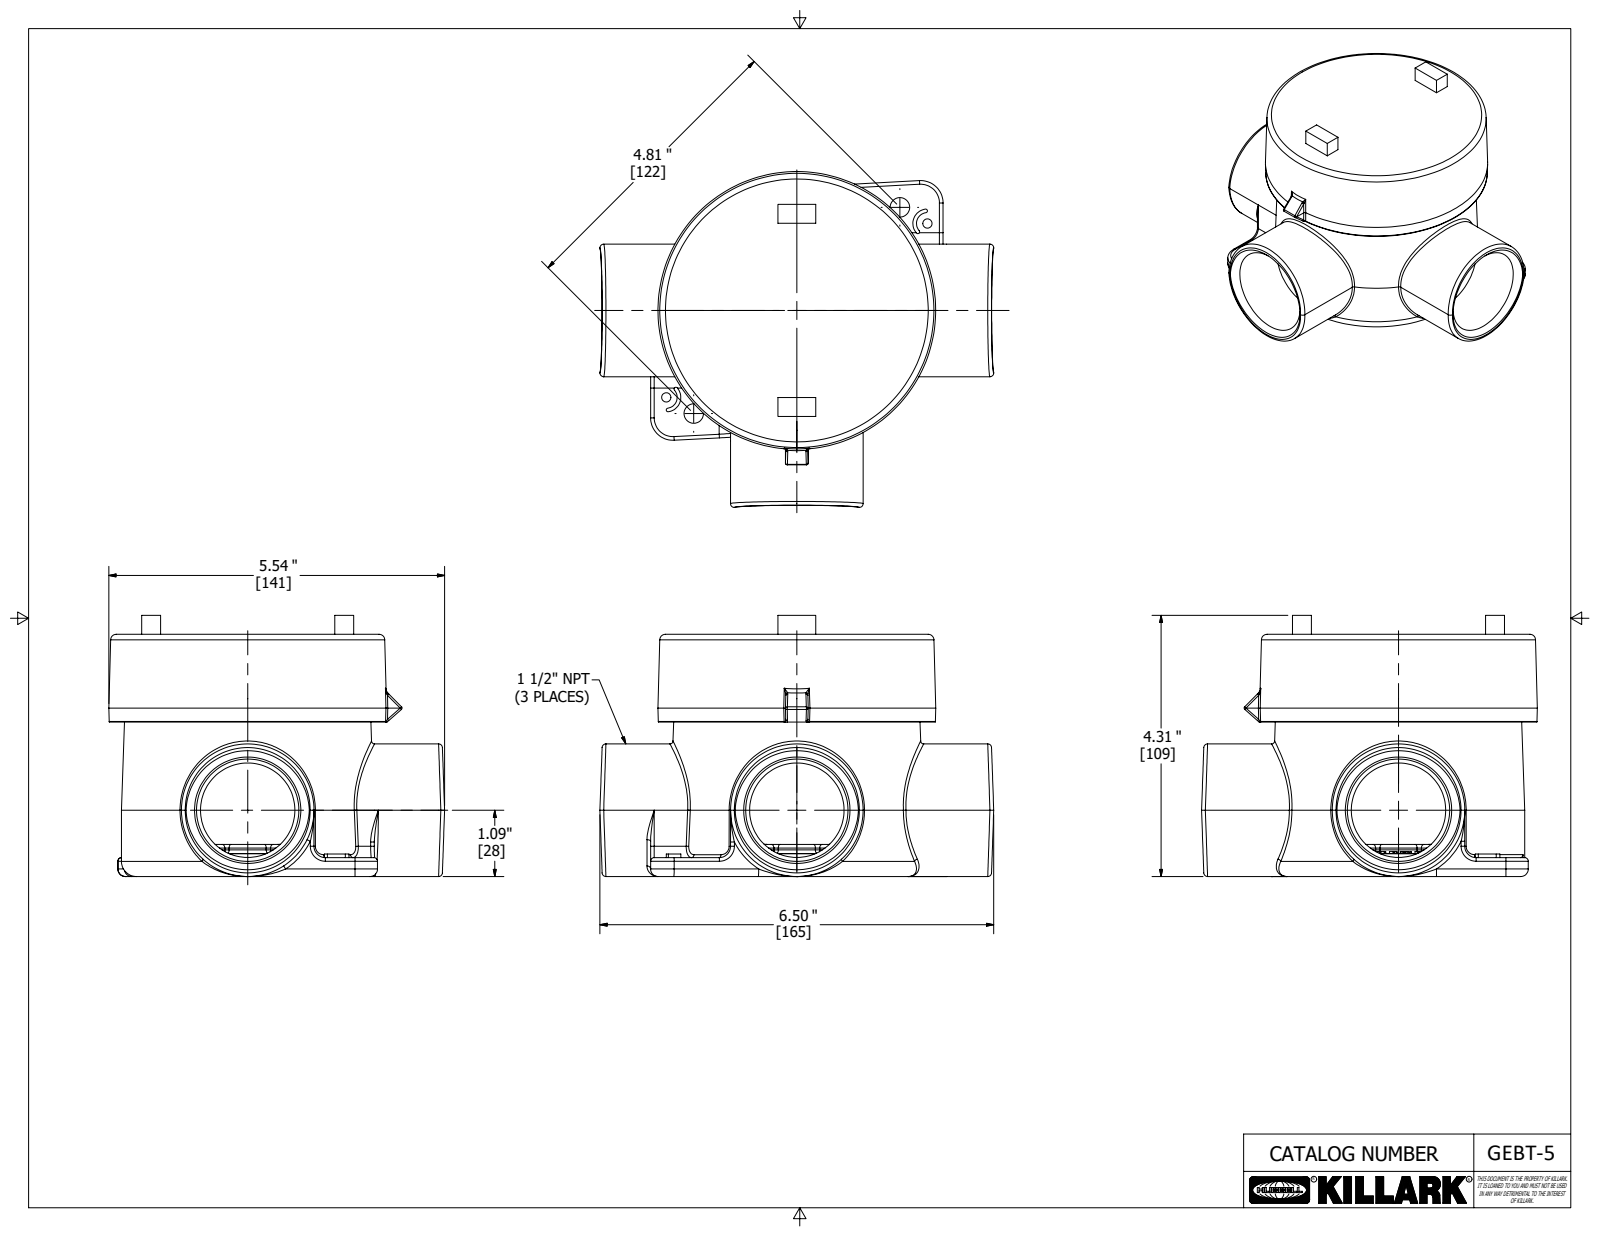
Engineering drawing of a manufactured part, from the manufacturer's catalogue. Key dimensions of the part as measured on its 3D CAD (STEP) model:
Part name (STEP PRODUCT): GEBT-5; 21158; 21147-override
STEP written by: Autodesk Inventor 2020 (AUTOMOTIVE_DESIGN)
Units: inches
Bodies: 2 solids, 845 faces (407 planar, 92 cylindrical, 346 other)
Overall size (bounding box): 6.5 × 5.542 × 4.31
Volume: 34.45 in³ · Surface area: 214 in²
Round holes (diameter × count): ⌀0.153 ×2, ⌀0.321 ×2, ⌀1.558 ×2, ⌀3.823 ×1, ⌀4.045 ×1
Round bosses / shafts (diameter × count): ⌀2.188 ×2
Partial cylindrical surfaces — rounded edges, fillets, slot ends (radius × count): R0.06 ×34, R0.03 ×14, R0.125 ×4, R0.031 ×3, R0.187 ×3, R0.18 ×2, R0.24 ×2, R0.37 ×2
Main face-to-face distances: 3.998, 3.56, 0.438, 2.549, 1.011, 1.449, 3.5, 0.38, 2.169, 3.18
Hole centre spacings: 0.527, 4.97, 2.406, 2.406, 2.589, 2.589, 4.812, 5.178
